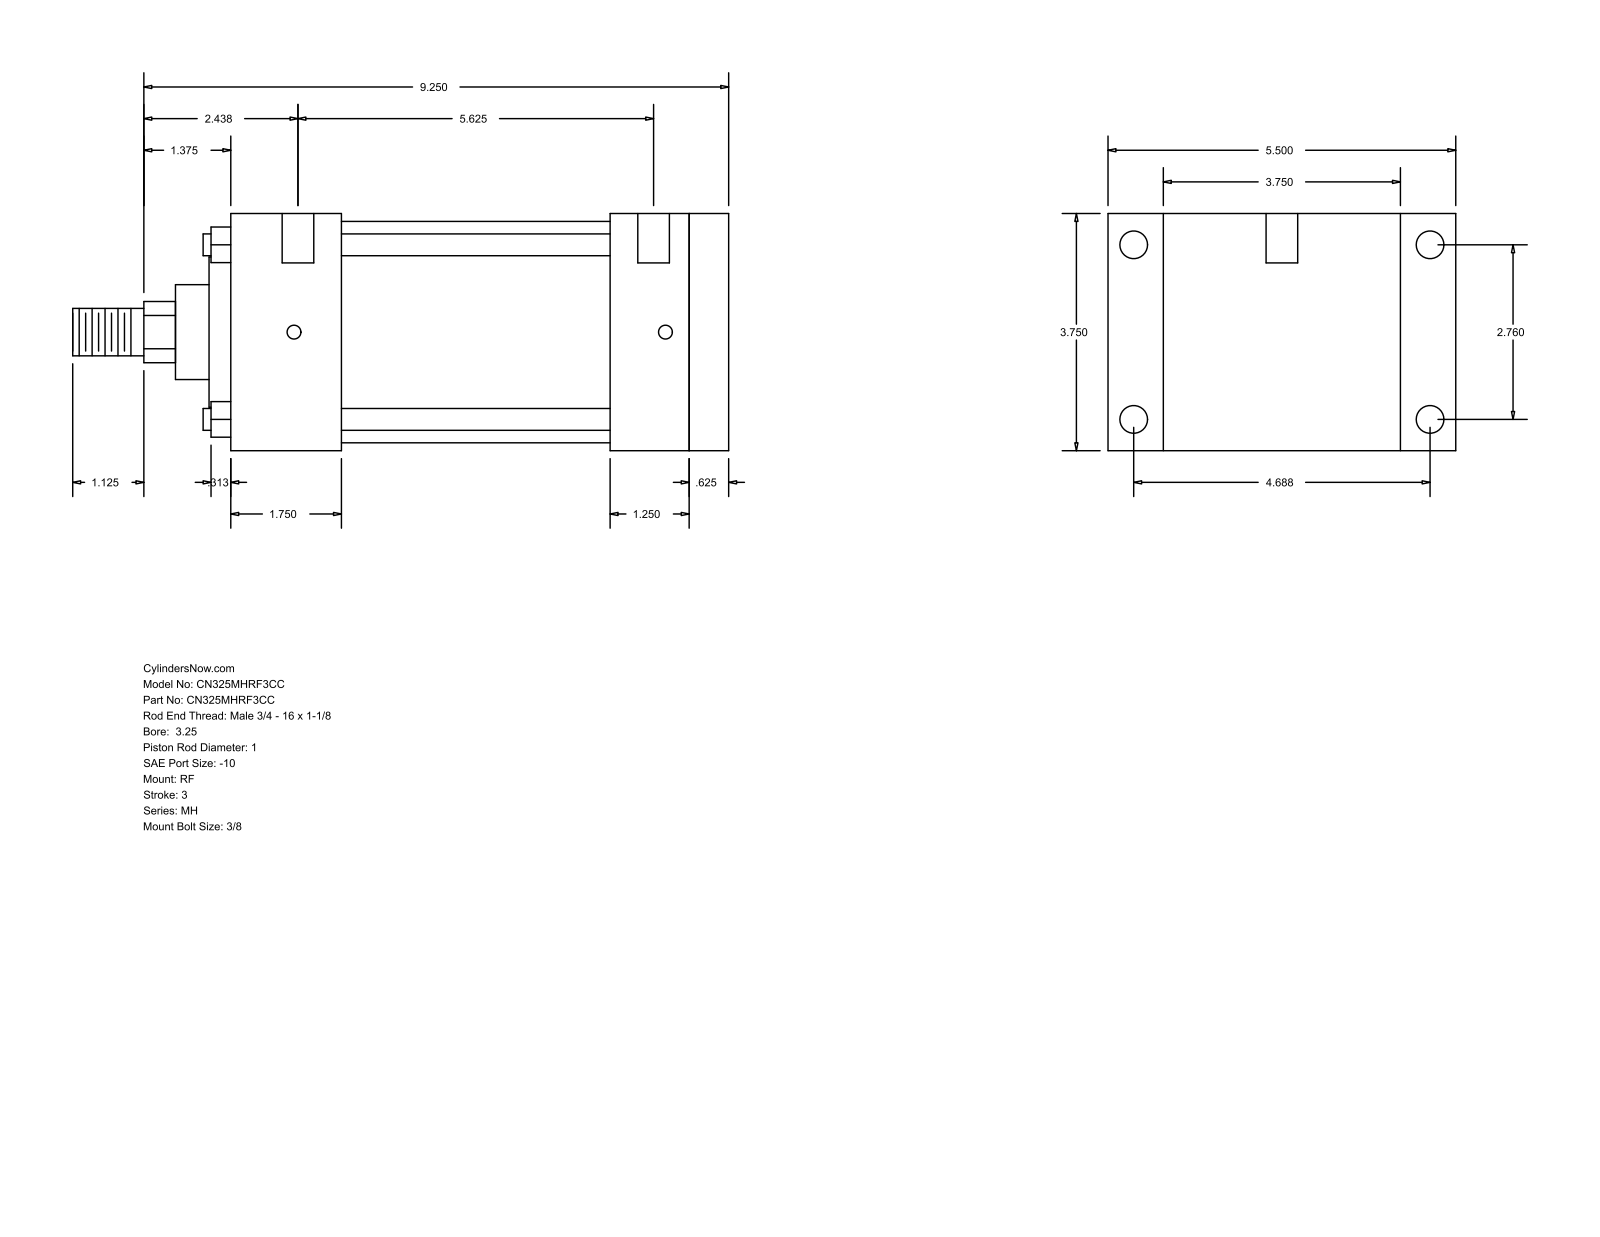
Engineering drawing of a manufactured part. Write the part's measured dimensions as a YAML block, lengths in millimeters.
part_name: "MH_RF__0325_1"
step_written_by: "GSSL Pune (CONFIG_CONTROL_DESIGN)"
units: millimeters
bodies: {solids: 0, faces: 94, planar: 65, cylindrical: 29, other: 0}
overall_size: [263.52, 139.7, 95.25]
round_holes:
  - {diameter: 5.56, count: 4}
  - {diameter: 11.13, count: 4}
  - {diameter: 12.7, count: 2}
round_bosses_or_shafts:
  - {diameter: 8.76, count: 4}
  - {diameter: 88.9, count: 1}
  - {diameter: 60.33, count: 1}
  - {diameter: 38.1, count: 1}
  - {diameter: 25.4, count: 1}
  - {diameter: 19.05, count: 1}
partial_cylinders:
  - {radius: 12.29, count: 1}
face_to_face_distances: [95.24, 200.03, 184.15, 15.88, 22.23, 117.47, 44.46, 139.69, 155.57, 152.4]
hole_center_spacings: [70.1, 119.06, 138.16, 149.22, 1.58, 4.76, 142.88, 144.46]
